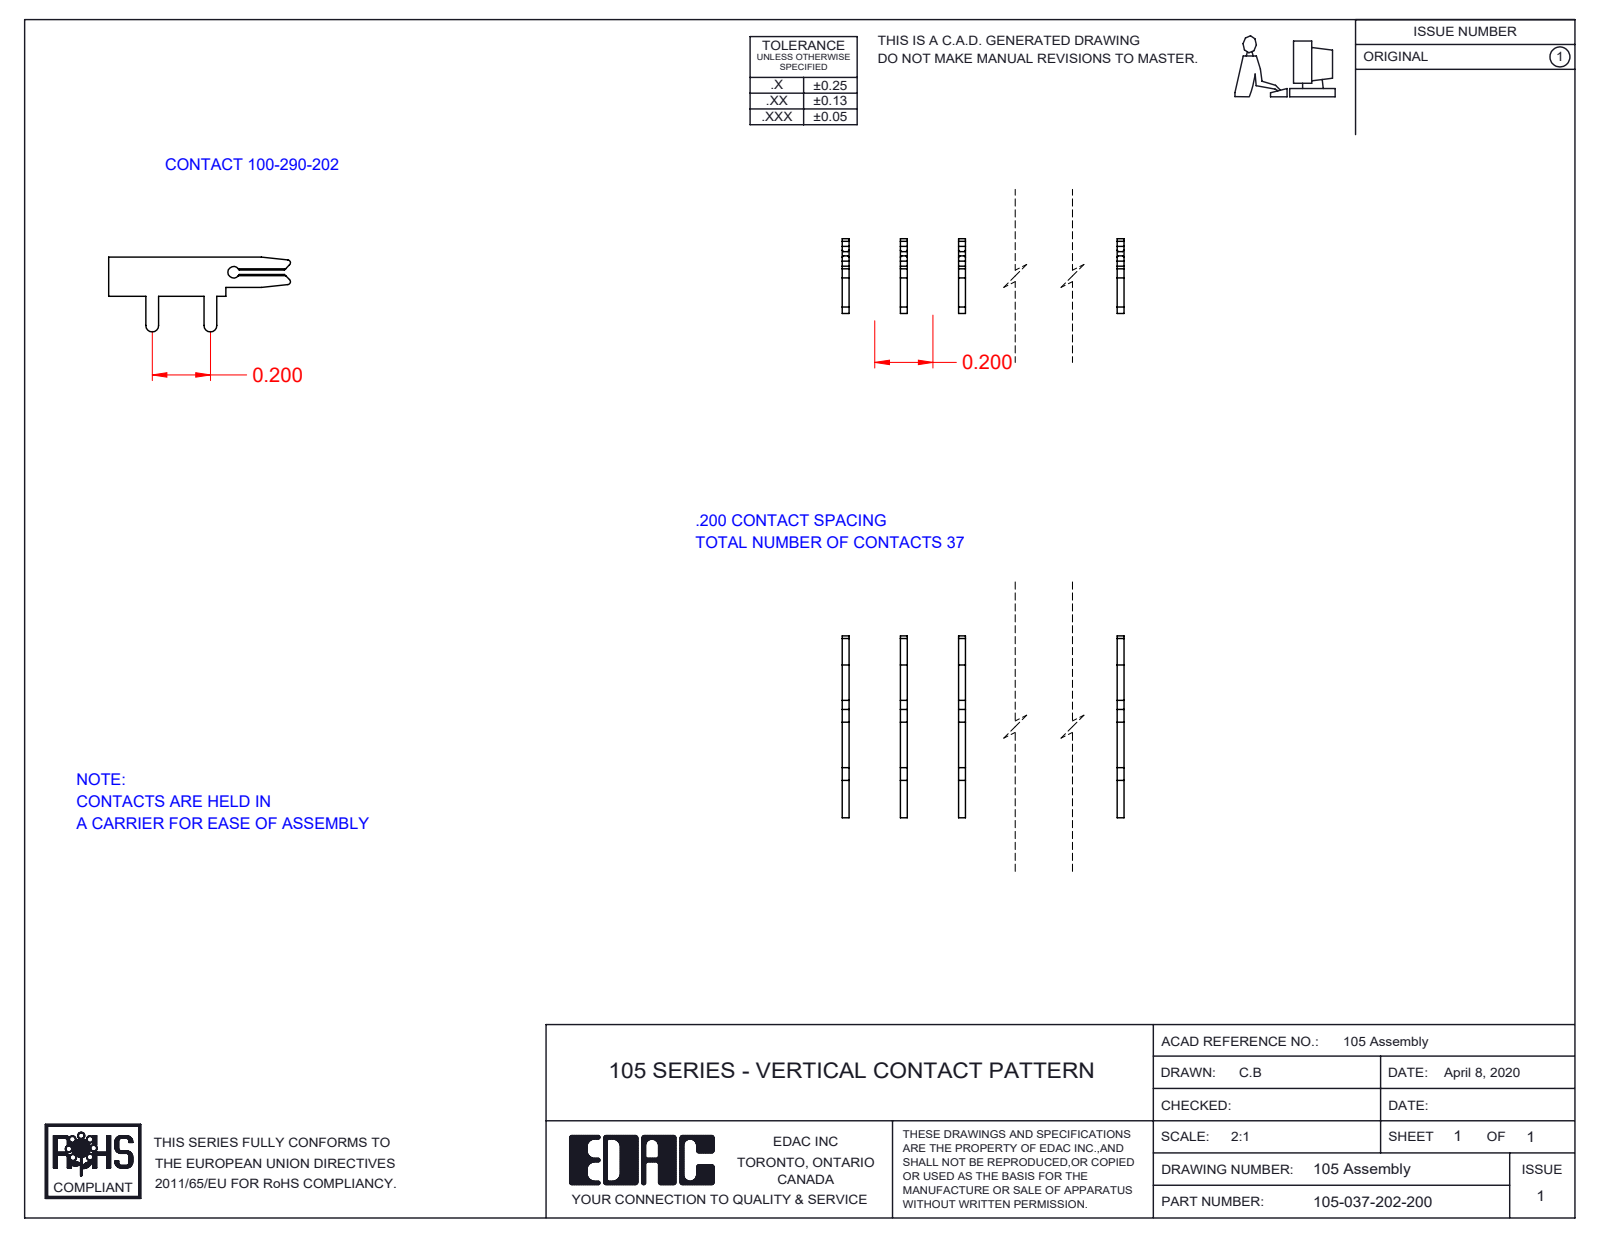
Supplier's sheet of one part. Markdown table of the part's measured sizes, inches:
| quantity | value |
| --- | --- |
| part name | 105-037-202-200; 100-290-001_100-290-202 |
| STEP written by | SolidWorks 2016 (CONFIG_CONTROL_DESIGN) |
| units | inches |
| bodies | 37 solids, 1110 faces (851 planar, 259 cylindrical, 0 other) |
| overall size | 7.224 × 0.625 × 0.257 |
| volume | 0.072 in³ |
| surface area | 8.104 in² |
| round holes (diameter × count) | 0.04 × 1 |
| partial cylindrical surfaces (radius × count) | 0.01 × 2, 0.022 × 2 |
| main face-to-face distances | 0.2, 0.4, 0.6, 0.8, 1, 1.2, 1.4, 1.6, 1.8, 2 |
